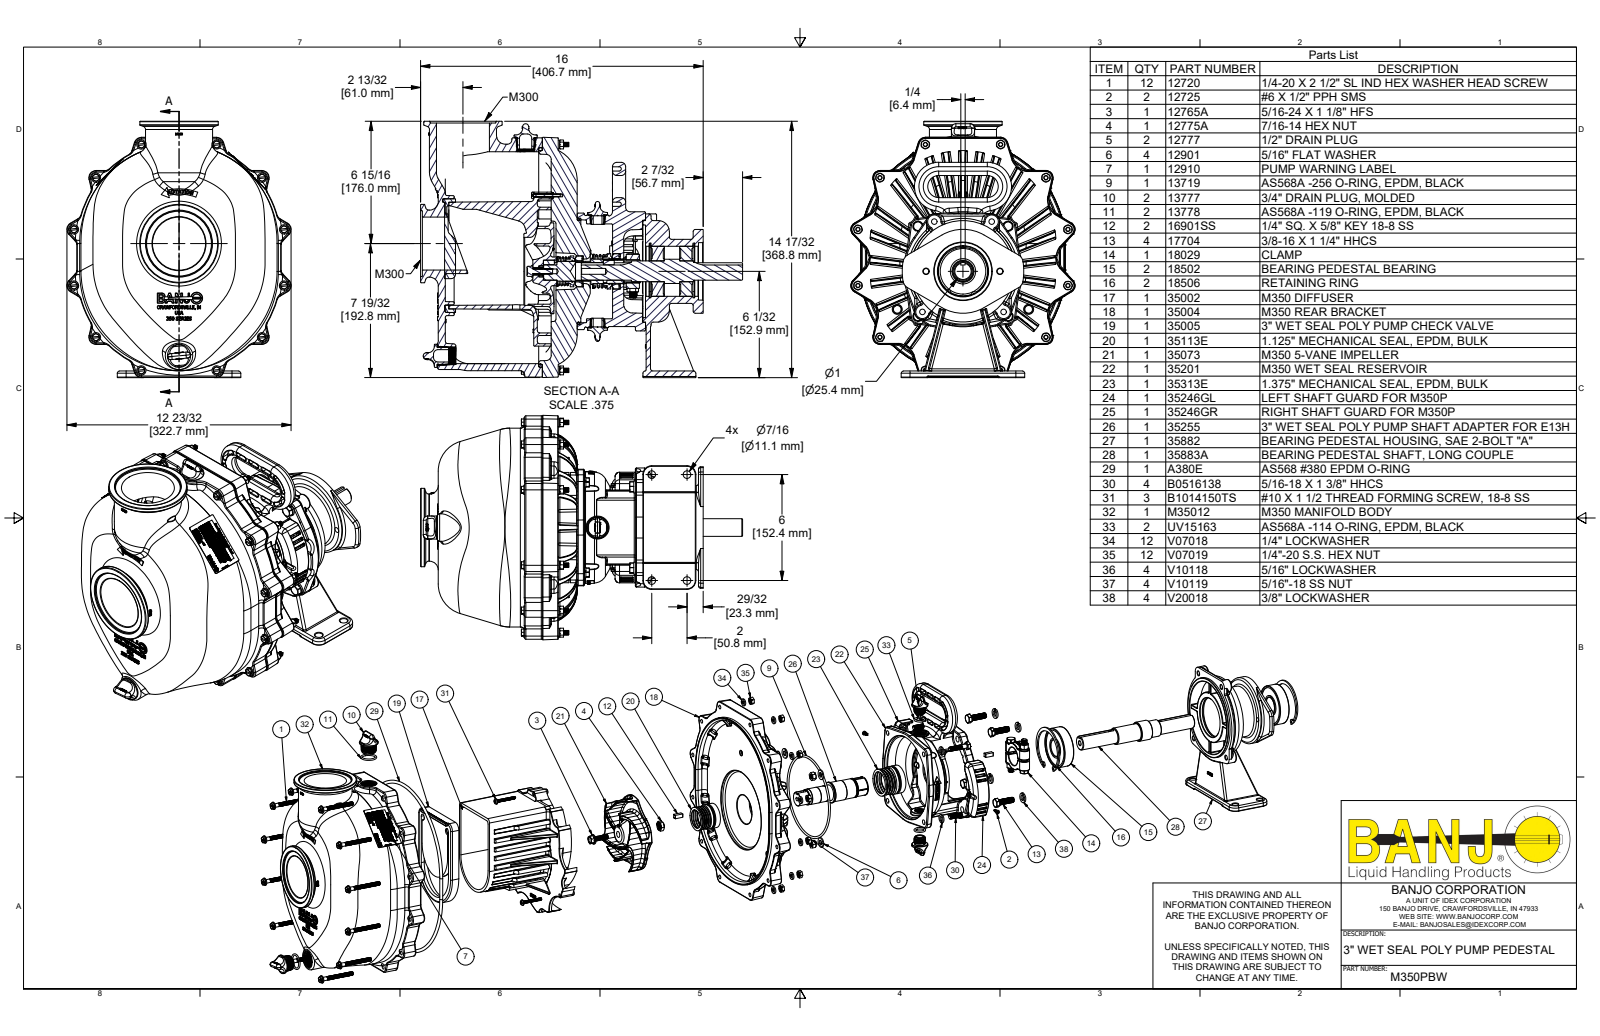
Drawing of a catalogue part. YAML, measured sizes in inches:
part_name: "M350PBW; 17704; 35073; 35002 (+8 more)"
step_written_by: "Autodesk Inventor 2022 (AUTOMOTIVE_DESIGN)"
units: inches
bodies: {solids: 110, faces: 25200, planar: 8749, cylindrical: 3995, other: 12456}
overall_size: [18.243, 14.518, 12.712]
volume: 404.9
surface_area: 2782
round_holes:
  - {diameter: 0.196, count: 12}
  - {diameter: 0.252, count: 12}
  - {diameter: 0.27, count: 12}
  - {diameter: 0.52, count: 10}
  - {diameter: 0.307, count: 6}
  - {diameter: 0.385, count: 6}
  - {diameter: 0.437, count: 5}
  - {diameter: 0.252, count: 4}
  - {diameter: 0.313, count: 4}
  - {diameter: 0.322, count: 4}
  - {diameter: 0.344, count: 4}
  - {diameter: 0.344, count: 4}
round_bosses_or_shafts:
  - {diameter: 0.324, count: 76}
  - {diameter: 0.337, count: 46}
  - {diameter: 0.489, count: 12}
  - {diameter: 0.25, count: 12}
  - {diameter: 0.687, count: 6}
  - {diameter: 0.375, count: 6}
  - {diameter: 0.721, count: 4}
  - {diameter: 0.688, count: 4}
partial_cylinders:
  - {radius: 0.031, count: 361}
  - {radius: 0.062, count: 212}
  - {radius: 0.125, count: 88}
  - {radius: 0.016, count: 75}
  - {radius: 0.094, count: 69}
  - {radius: 0.25, count: 58}
  - {radius: 0.03, count: 54}
  - {radius: 0.375, count: 46}
face_to_face_distances: [0.4, 6.4, 0.5, 0.9, 5.014, 0.2, 0.269, 6.669, 1.386, 0.986]
hole_center_spacings: [6.005, 3.182, 9.407, 3.611, 5.107, 6.137, 6.236, 6.408]
